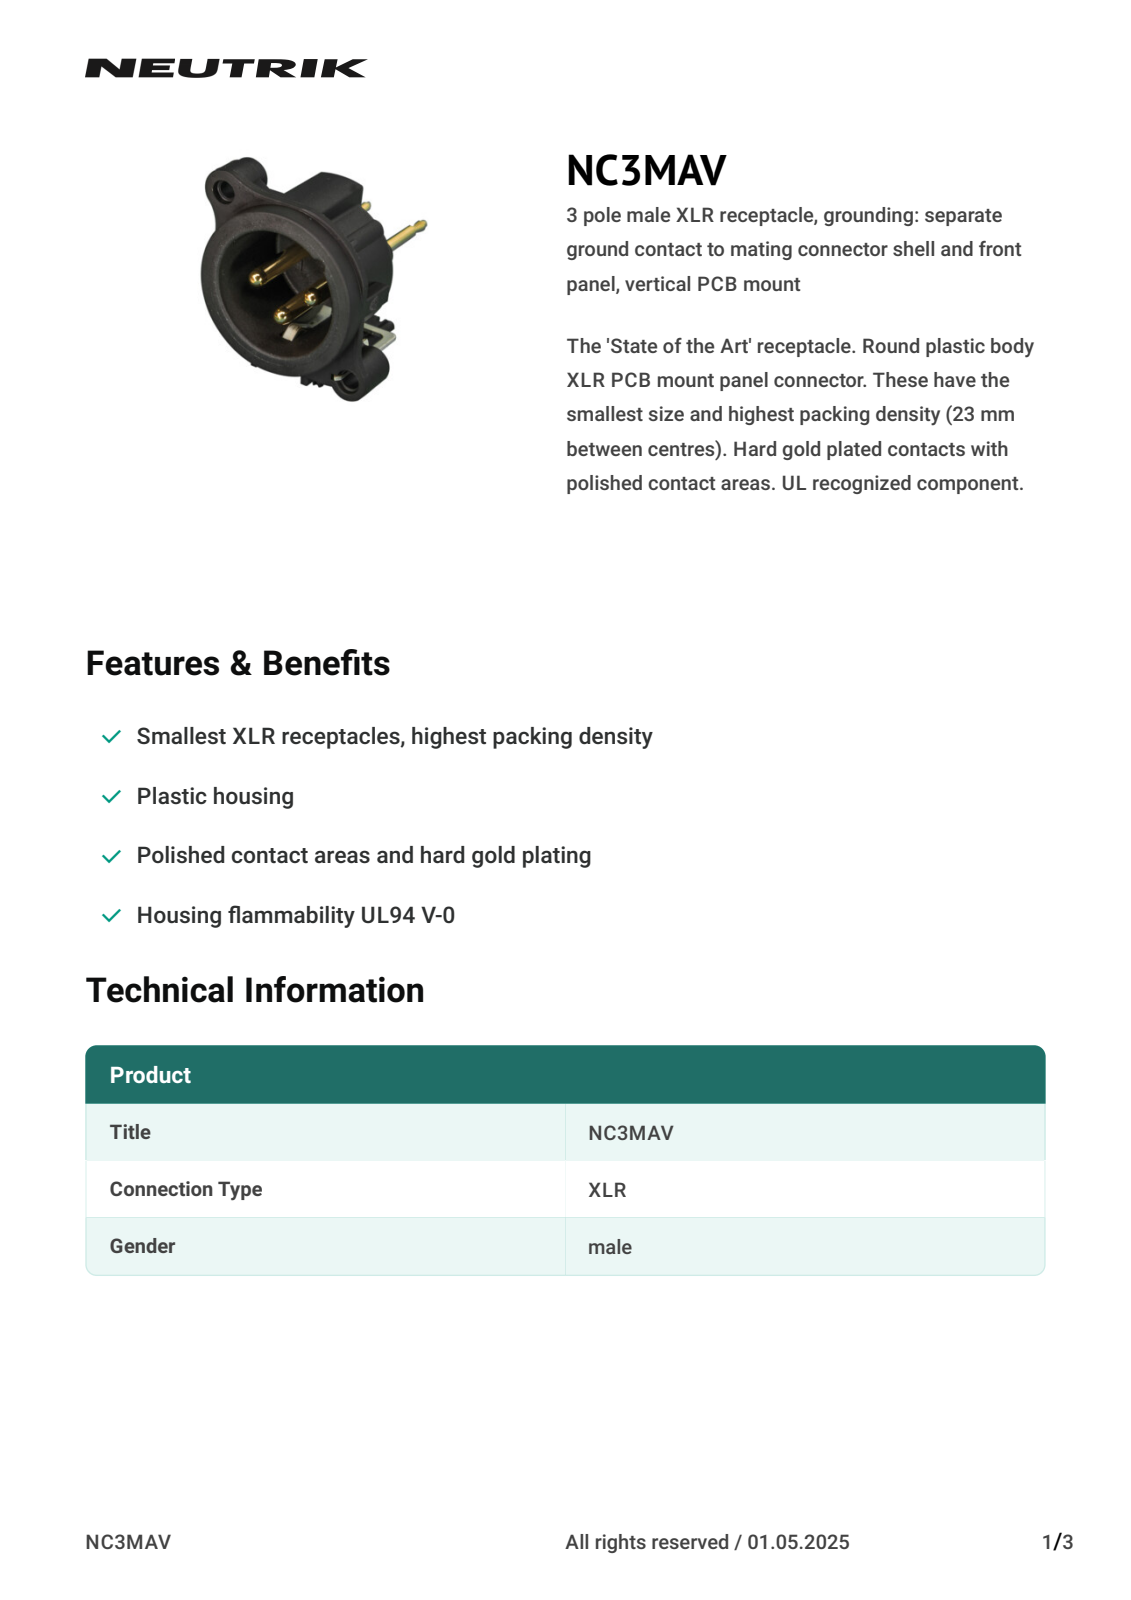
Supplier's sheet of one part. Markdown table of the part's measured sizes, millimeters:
| quantity | value |
| --- | --- |
| part name | 30013093 |
| STEP written by | CREO PARAMETRIC BY PTC INC, 2023424 (CONFIG_CONTROL_DESIGN) |
| units | millimeters |
| bodies | 1 solid, 950 faces (391 planar, 217 cylindrical, 342 other) |
| overall size | 30.2 × 26.8 × 25.3 |
| volume | 2 609 mm³ |
| surface area | 4 446 mm² |
| round holes (diameter × count) | 2.3 × 2, 2.5 × 1, 3.2 × 1 |
| round bosses / shafts (diameter × count) | 2.38 × 3, 1.8 × 3, 1.7 × 3, 1 × 3, 1.5 × 2, 21.8 × 1, 5.8 × 1, 5.2 × 1 |
| partial cylindrical surfaces (radius × count) | 0.3 × 69, 0.2 × 24, 0.5 × 11, 0.12 × 9, 1 × 5, 0.4 × 4, 0.75 × 3, 0.19 × 2 |
| main face-to-face distances | 1, 13.4, 14.4, 10.7, 2.7, 1.28, 11.7, 0.5, 3.7, 9.7 |
| hole center spacings | 10.92, 18.14, 28 |
